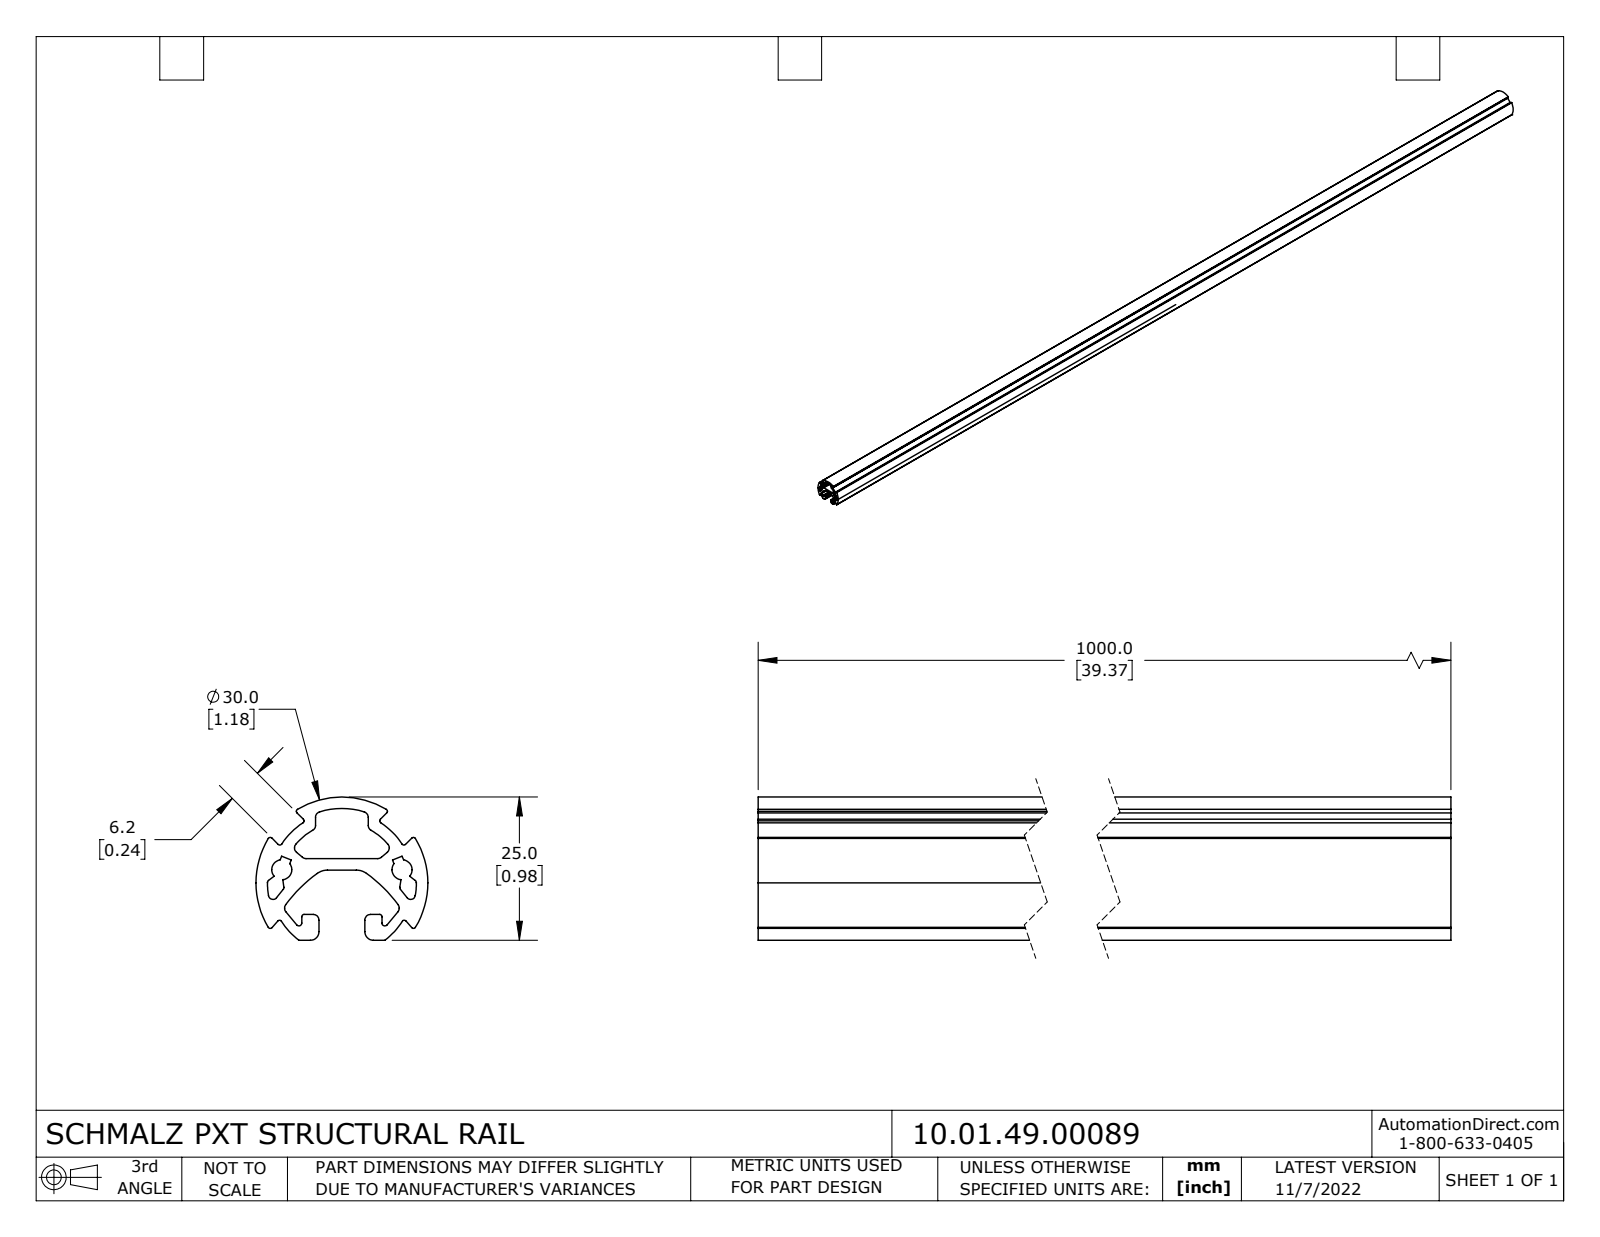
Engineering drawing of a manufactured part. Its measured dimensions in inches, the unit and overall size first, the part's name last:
Units: inches
Overall size (bounding box): 39.37 × 1.181 × 0.984
Partial cylindrical surfaces — rounded edges, fillets, slot ends (radius × count): R0.016 ×14, R0.039 ×12, R0.02 ×6, R0.031 ×2, R0.059 ×2, R0.069 ×2, R0.118 ×2, R0.984 ×2
Main face-to-face distances: 0.079, 0.482, 0.561, 0.177, 0.305, 0.384, 0.244, 0.024, 0.339, 0.094
Volume: 16.85 in³ · Surface area: 353 in²
Bodies: 1 solid, 101 faces (36 planar, 65 cylindrical, 0 other)
Part name (STEP PRODUCT): 10.01.49.00089
STEP written by: SolidWorks 2021 (CONFIG_CONTROL_DESIGN)
